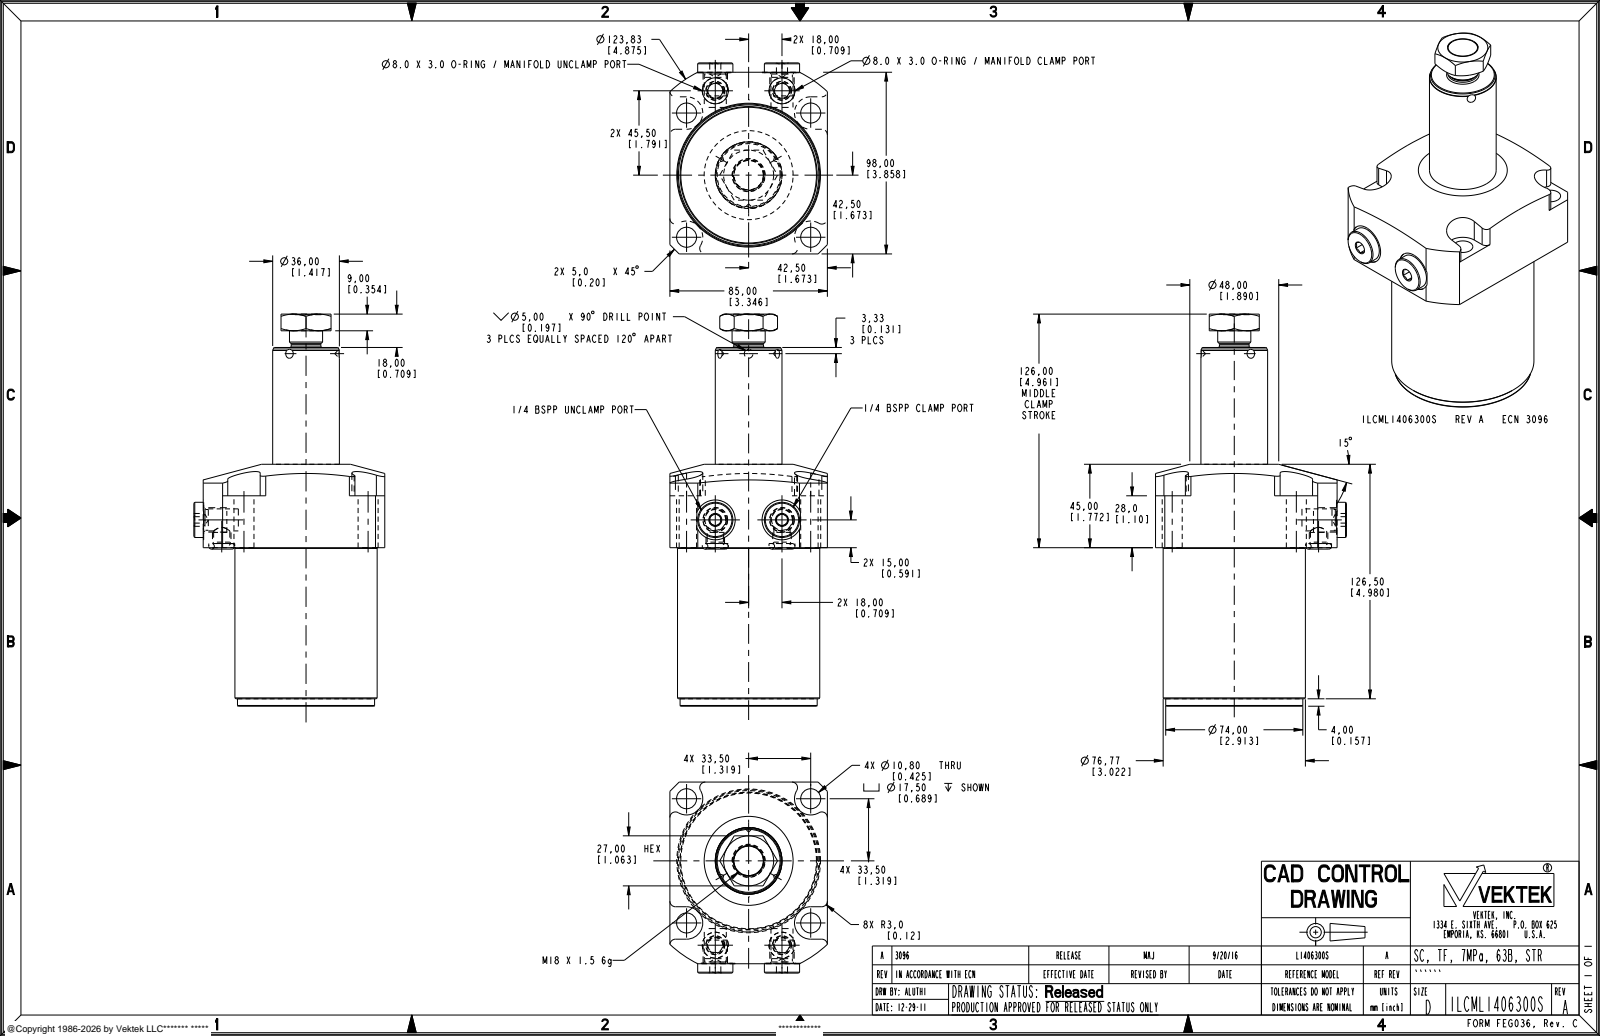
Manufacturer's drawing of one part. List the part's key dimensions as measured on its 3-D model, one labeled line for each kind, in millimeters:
Part name (STEP PRODUCT): ILCML1406300S
STEP written by: PRO/ENGINEER BY PARAMETRIC TECHNOLOGY CORPORATION, 2013320 (AUTOMOTIVE_DESIGN)
Units: millimetres
Bodies: 3 solids, 205 faces (68 planar, 68 cylindrical, 69 other)
Overall size (bounding box): 211.5 × 103.05 × 85
Volume: 781 654 mm³ · Surface area: 68 512 mm²
Round holes (diameter × count): ⌀10.8 ×4, ⌀6 ×2, ⌀8.75 ×2, ⌀11.89 ×2, ⌀14 ×2, ⌀21.5 ×2, ⌀16.5 ×1
Round bosses / shafts (diameter × count): ⌀19 ×2, ⌀13.16 ×2, ⌀11.2 ×2, ⌀10 ×2, ⌀76.77 ×1, ⌀74 ×1, ⌀36 ×1, ⌀17.87 ×1
Partial cylindrical surfaces — rounded edges, fillets, slot ends (radius × count): R3 ×8, R8.75 ×4, R61.91 ×1
Main face-to-face distances: 85, 85.5, 98, 28, 130.5, 45, 113.5, 17, 18, 193.5
Hole centre spacings: 47.38, 67, 19.6, 36, 48.93, 52.88, 80.51, 94.3
